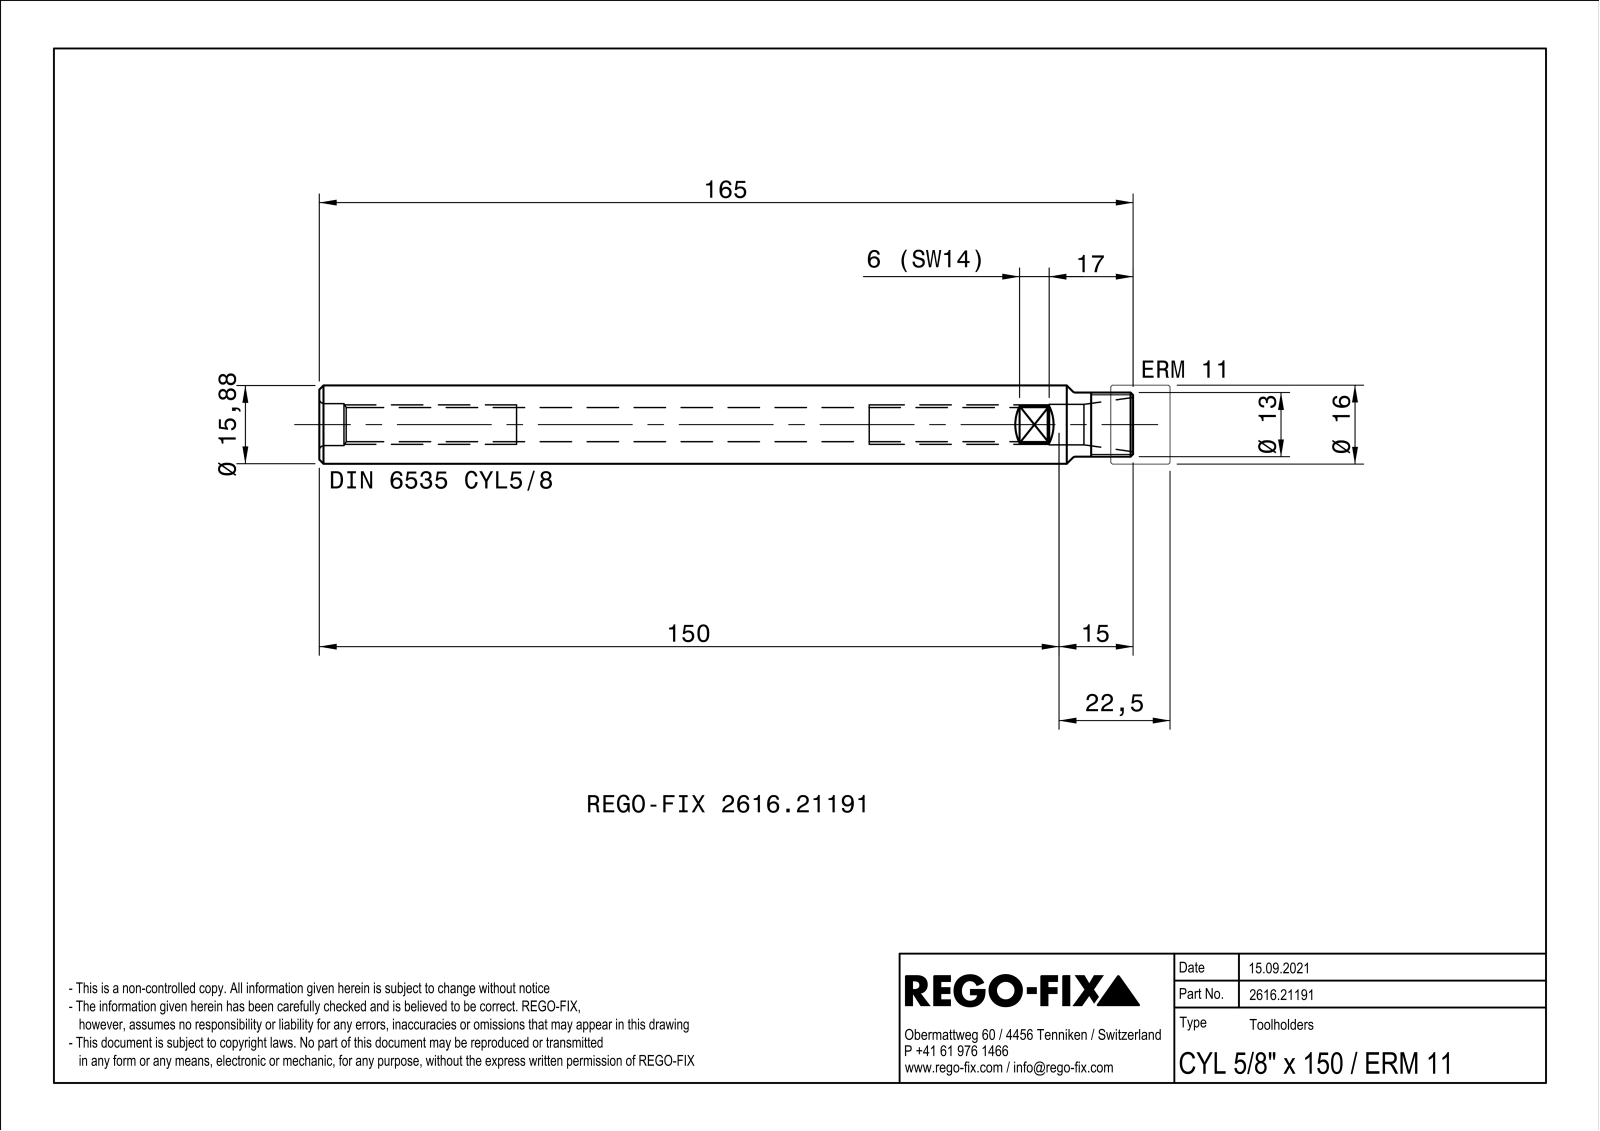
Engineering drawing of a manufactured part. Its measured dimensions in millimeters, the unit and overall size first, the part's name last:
Units: millimetres
Overall size (bounding box): 165 × 15.88 × 15.88
Round holes (diameter × count): ⌀6.92 ×1, ⌀8.2 ×1, ⌀8.5 ×1
Round bosses / shafts (diameter × count): ⌀15.87 ×1, ⌀13 ×1
Main face-to-face distances: 14, 5.66, 165
Volume: 24 974 mm³ · Surface area: 12 018 mm²
Bodies: 1 solid, 25 faces (8 planar, 8 cylindrical, 9 other)
Part name (STEP PRODUCT): NOCUT
STEP written by: SIEMENS PLM Software Solid Edge ST10 (AUTOMOTIVE_DESIGN)
